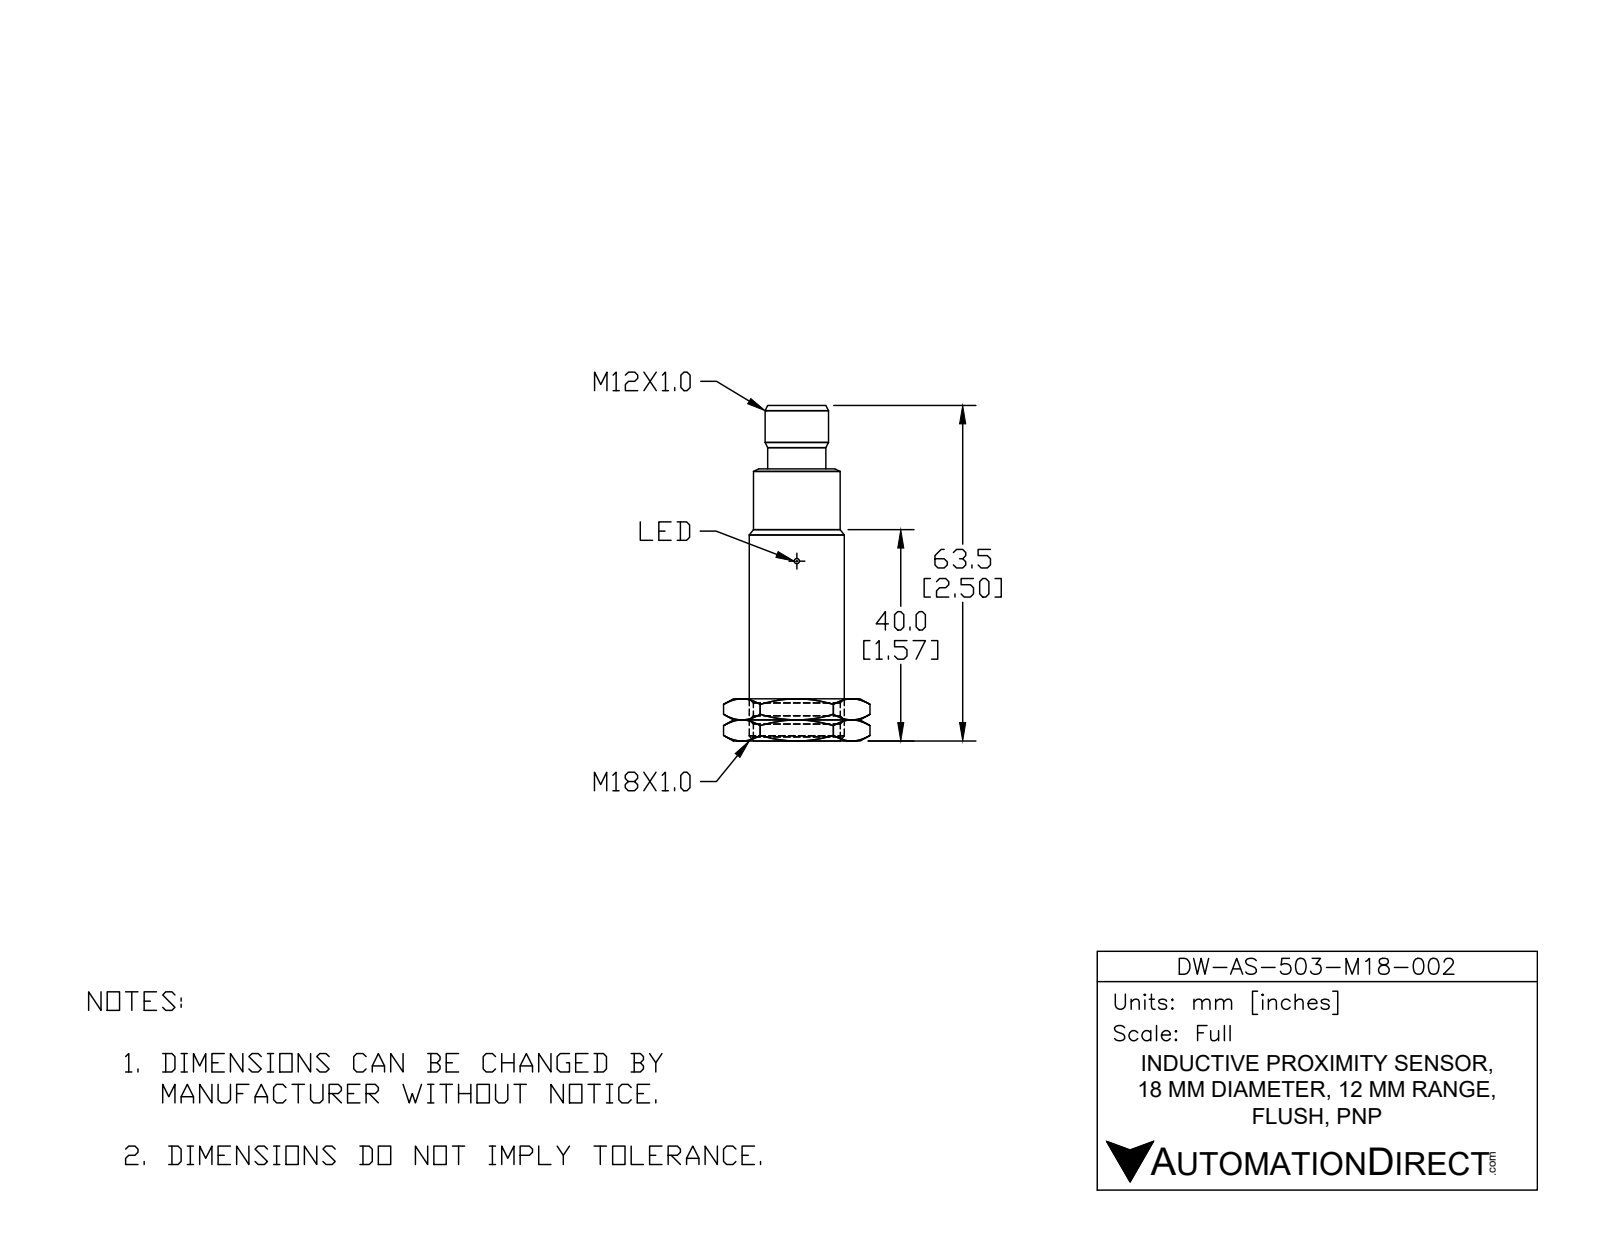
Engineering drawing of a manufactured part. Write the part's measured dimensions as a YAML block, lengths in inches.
part_name: "DW-AS-503-M18-002"
step_written_by: "SolidWorks 2017 (AUTOMOTIVE_DESIGN)"
units: inches
bodies: {solids: 1, faces: 38, planar: 8, cylindrical: 20, other: 10}
overall_size: [2.505, 0.709, 0.709]
volume: 0.813
surface_area: 6.395
round_holes:
  - {diameter: 0.118, count: 2}
  - {diameter: 0.335, count: 1}
round_bosses_or_shafts:
  - {diameter: 0.039, count: 4}
  - {diameter: 0.709, count: 1}
  - {diameter: 0.646, count: 1}
  - {diameter: 0.472, count: 1}
  - {diameter: 0.415, count: 1}
partial_cylinders:
  - {radius: 0.022, count: 2}
  - {radius: 0.193, count: 1}
face_to_face_distances: [1.99, 2.163, 0.172, 2.505, 0.515, 0.343, 0.043, 1.635, 0.355, 0.527]
